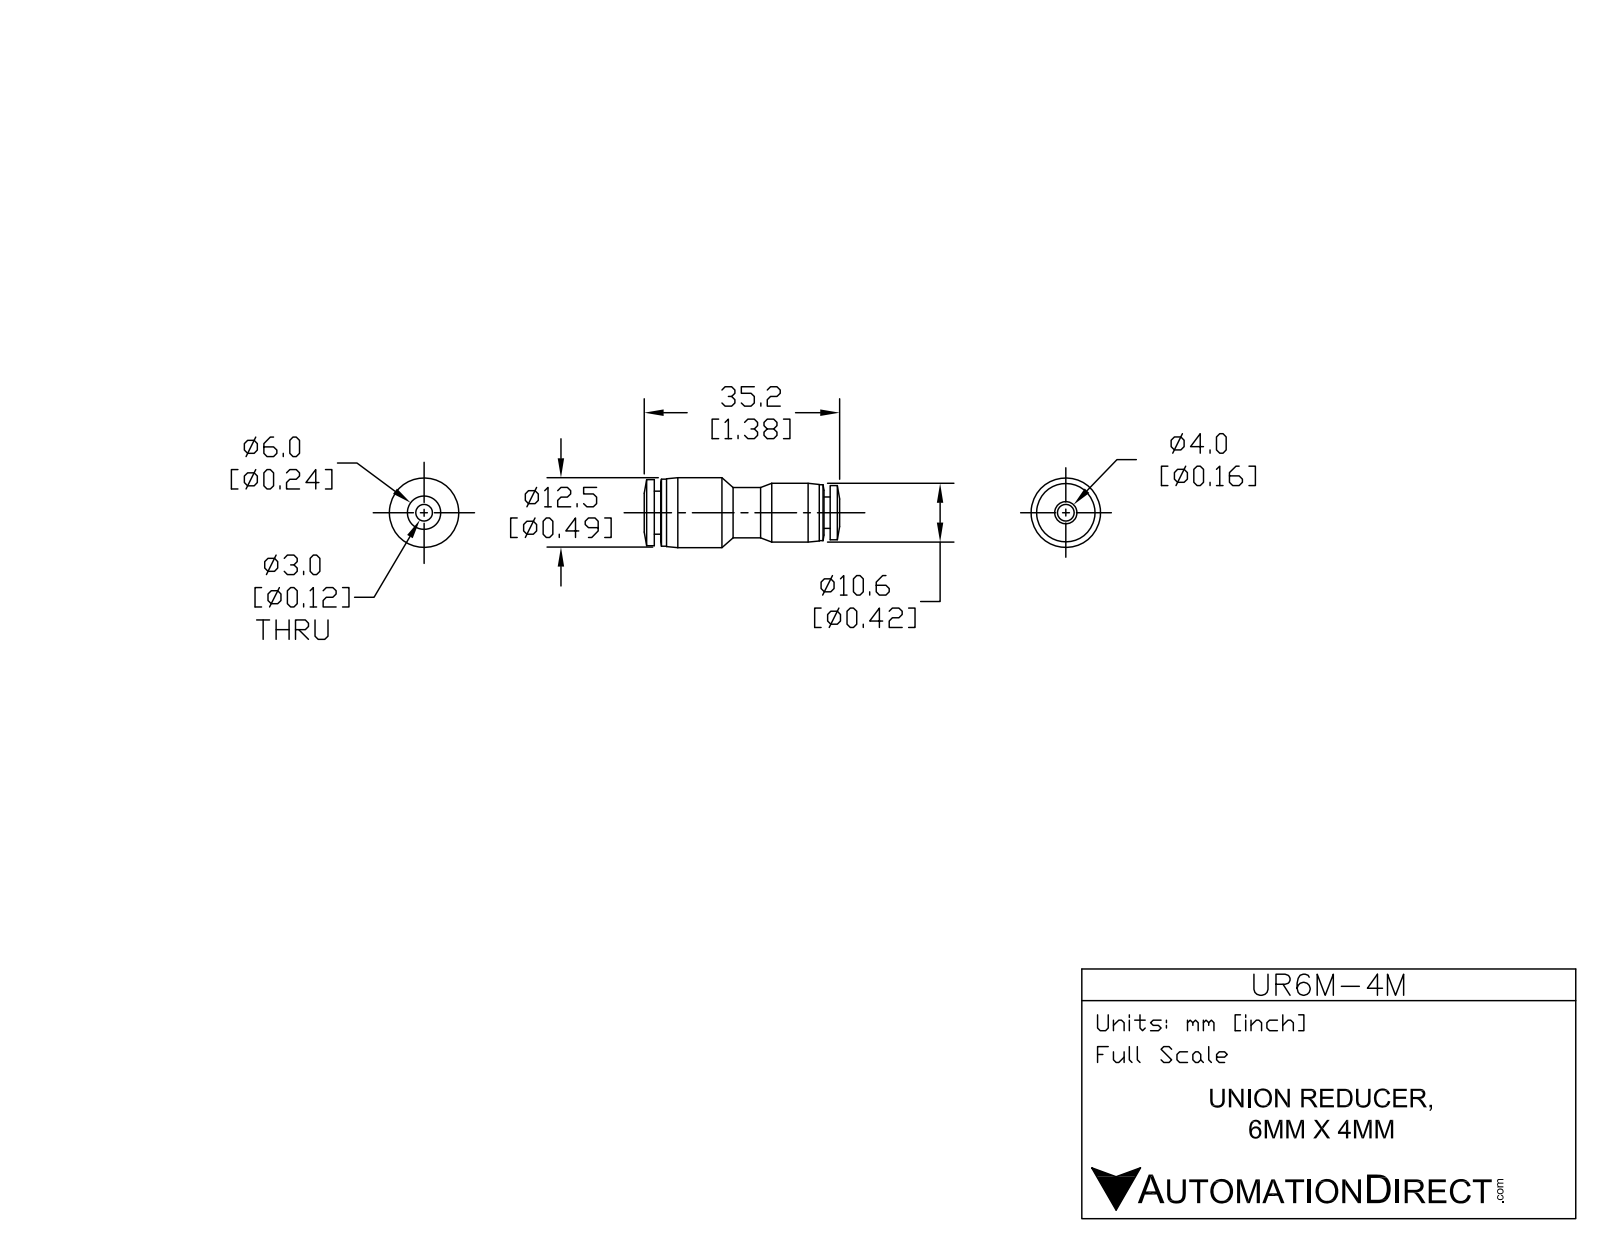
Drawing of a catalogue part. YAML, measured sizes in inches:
part_name: "UR6M-4M"
step_written_by: "SolidWorks 2015 (AUTOMOTIVE_DESIGN)"
units: inches
bodies: {solids: 1, faces: 54, planar: 10, cylindrical: 24, other: 20}
overall_size: [1.376, 0.492, 0.492]
volume: 0.146
surface_area: 3.288
round_holes:
  - {diameter: 0.118, count: 1}
  - {diameter: 0.169, count: 1}
  - {diameter: 0.248, count: 1}
round_bosses_or_shafts:
  - {diameter: 0.492, count: 1}
  - {diameter: 0.472, count: 1}
  - {diameter: 0.465, count: 1}
  - {diameter: 0.413, count: 1}
  - {diameter: 0.394, count: 1}
  - {diameter: 0.382, count: 1}
  - {diameter: 0.354, count: 1}
  - {diameter: 0.303, count: 1}
face_to_face_distances: [1.238, 1.193, 0.045, 0.043, 1.15, 1.195, 0.663, 0.62, 0.53, 0.575]
